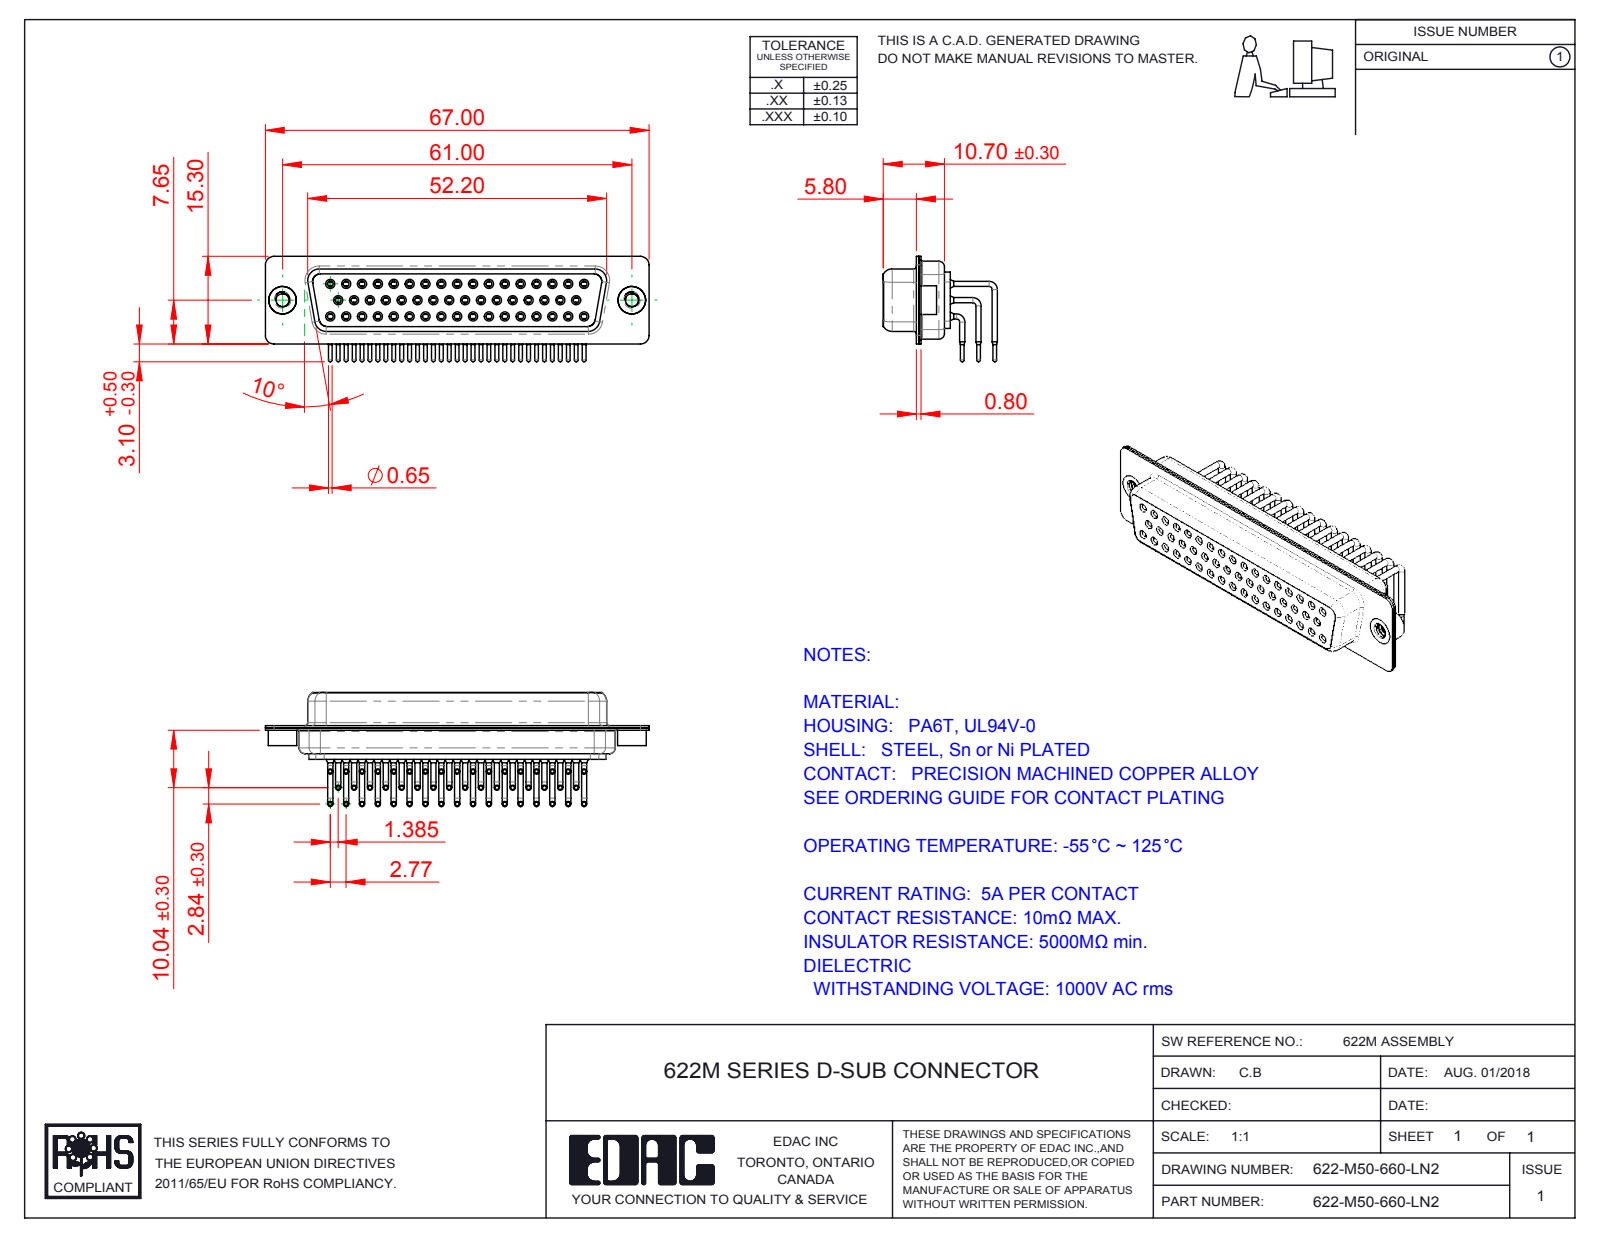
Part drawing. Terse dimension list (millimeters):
name: 622M Shell Rear_50 Contacts; 622M Shell Front_50 Contacts; 622M Housing_50 Contacts; 622-M50-660-LN2 (+4 more)
written by: SolidWorks 2016 (CONFIG_CONTROL_DESIGN)
unit: mm
bodies: 55 solids, 2929 faces (817 planar, 1287 cylindrical, 825 other)
size: 67 × 19.93 × 18.4
volume: 6 933 mm³; area: 16 132 mm²
holes: 50× ⌀1, 50× ⌀1.1, 50× ⌀1.7, 50× ⌀1.8, 50× ⌀2, 2× ⌀2.26, 2× ⌀4, 2× ⌀4.8
bosses: 100× ⌀0.9, 50× ⌀1.6, 50× ⌀1.5, 50× ⌀0.65, 2× ⌀5, 2× ⌀4.9
rounds: 16× R1.5, 12× R2, 8× R1.35, 8× R1.6, 4× R0.25, 4× R0.5, 4× R0.6, 4× R0.65
face distances: 0.4, 1.35, 11.85, 0.85, 2.2, 5.5, 12.25, 5.9, 10.5, 0.8
hole spacings: 2.77, 3.16, 5.54, 8.31, 11.08, 13.85, 16.62, 19.39
